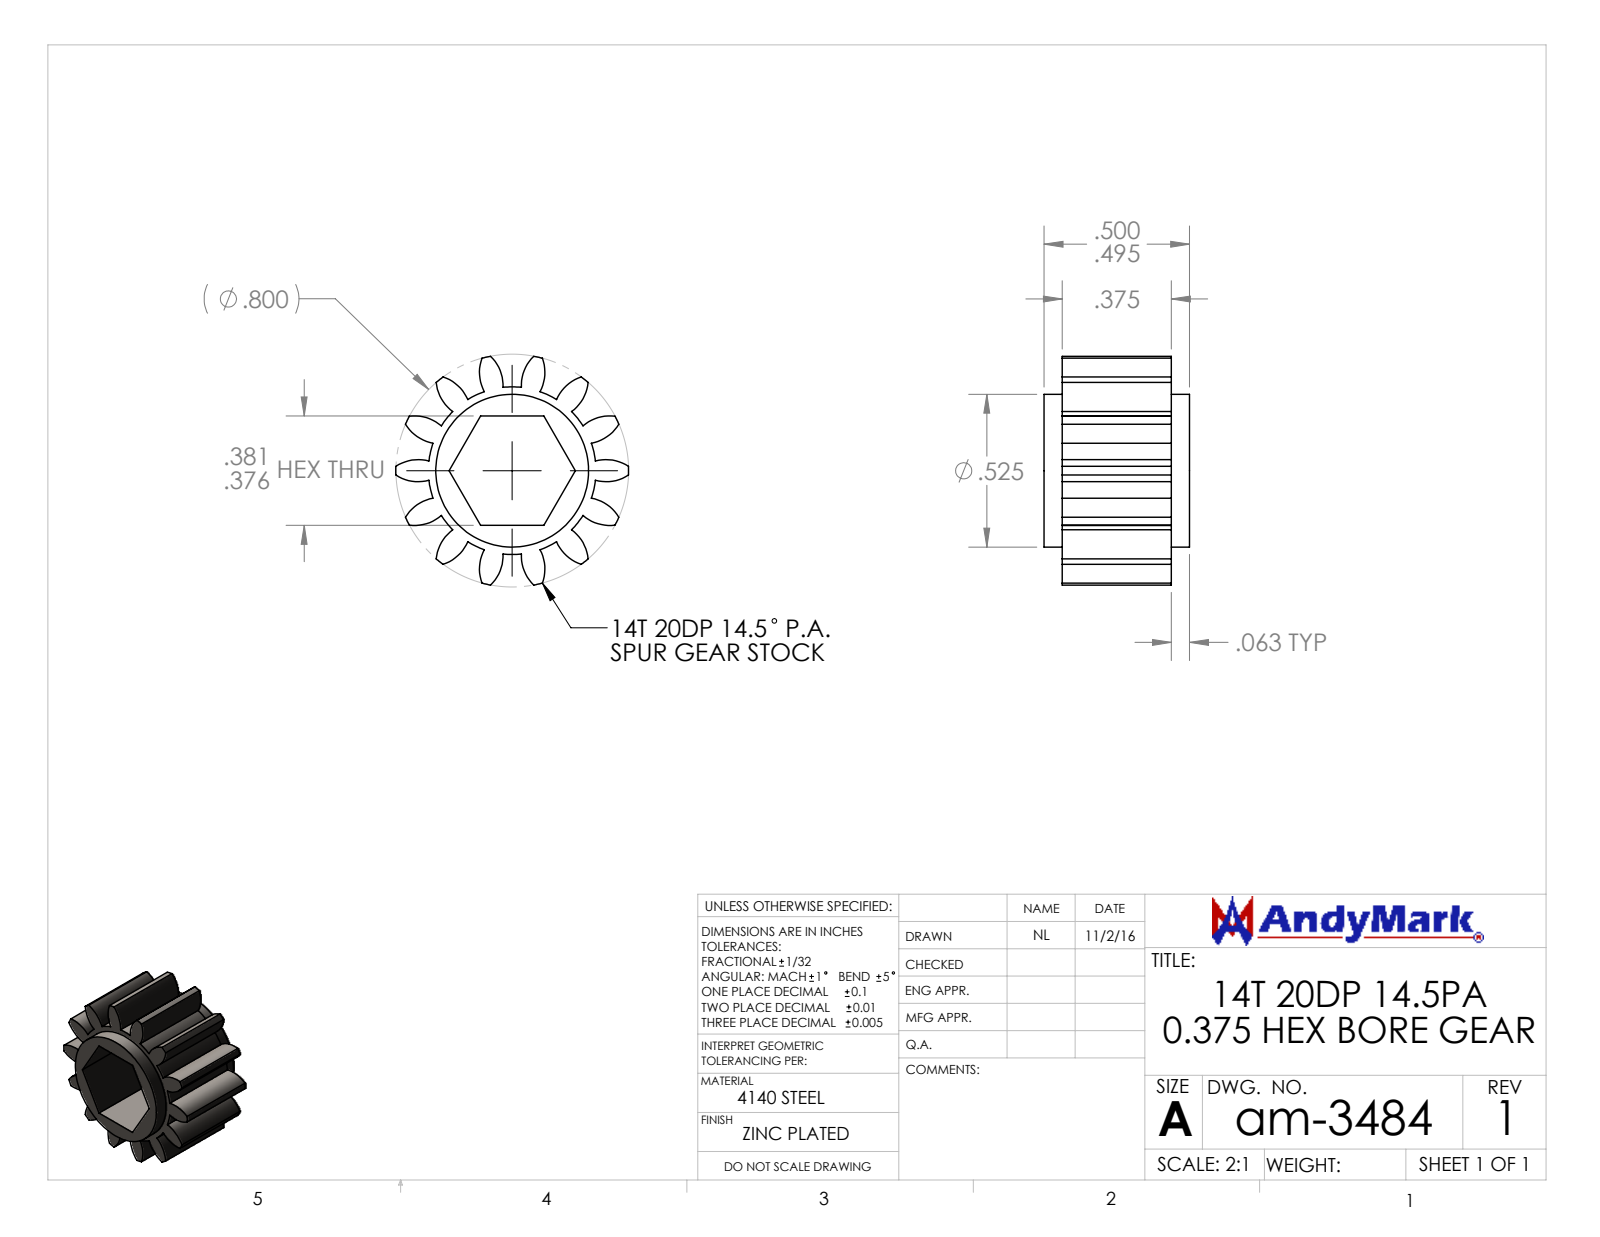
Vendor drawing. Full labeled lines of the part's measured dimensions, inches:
Part name (STEP PRODUCT): am-3484 14T 20dp 375hex 375 FW
STEP written by: SolidWorks 2014 (AUTOMOTIVE_DESIGN)
Units: inches
Bodies: 1 solid, 75 faces (10 planar, 65 cylindrical, 0 other)
Overall size (bounding box): 0.8 × 0.786 × 0.5
Volume: 0.102 in³ · Surface area: 3.073 in²
Round bosses / shafts (diameter × count): ⌀0.525 ×1
Partial cylindrical surfaces — rounded edges, fillets, slot ends (radius × count): R0.14 ×28, R0.288 ×1, R0.4 ×1
Main face-to-face distances: 0.376, 0.375, 0.063, 0.438, 0.5, 0.437, 0.062
